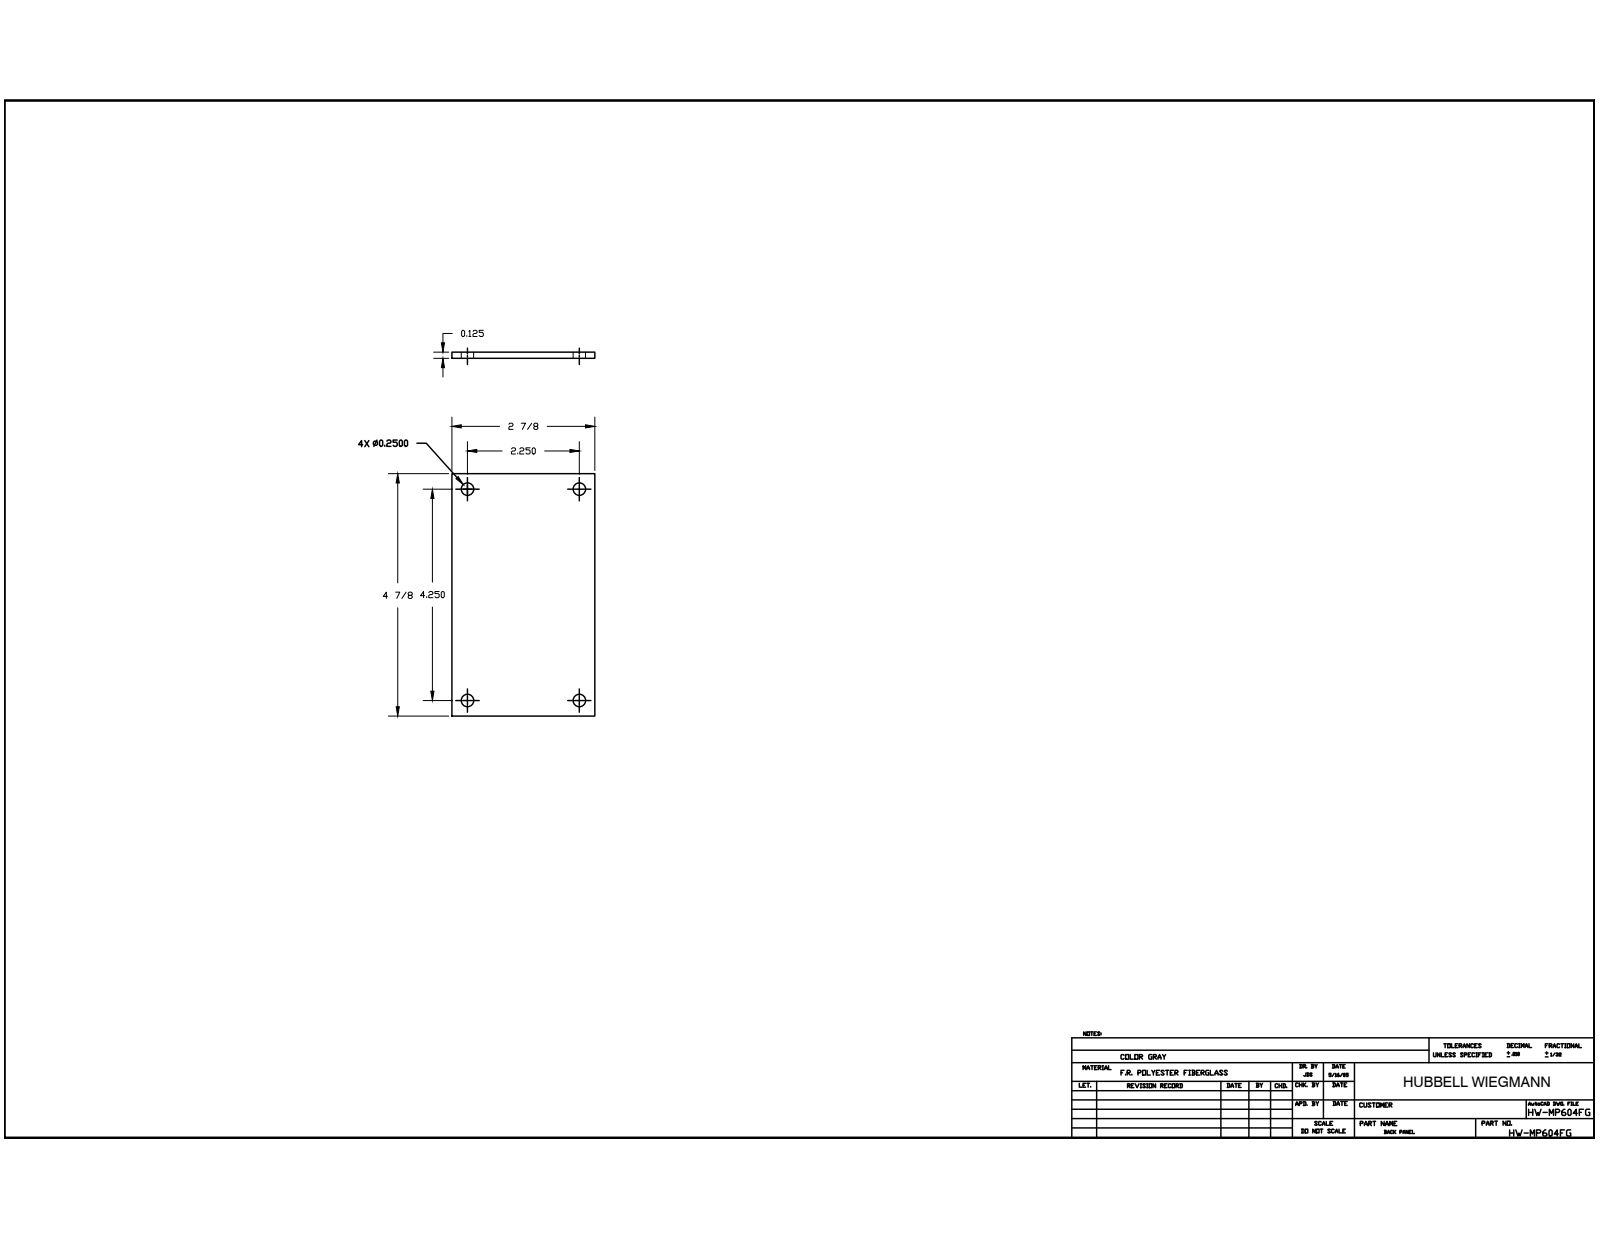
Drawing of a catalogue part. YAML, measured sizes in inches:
part_name: "BP64FG_STP"
step_written_by: "Autodesk Inventor 2014 (AUTOMOTIVE_DESIGN)"
units: inches
bodies: {solids: 1, faces: 10, planar: 6, cylindrical: 4, other: 0}
overall_size: [4.88, 2.88, 0.125]
volume: 1.732
surface_area: 30.05
round_holes:
  - {diameter: 0.25, count: 4}
face_to_face_distances: [0.125, 2.88, 4.88]
hole_center_spacings: [2.25, 4.25, 4.809]
